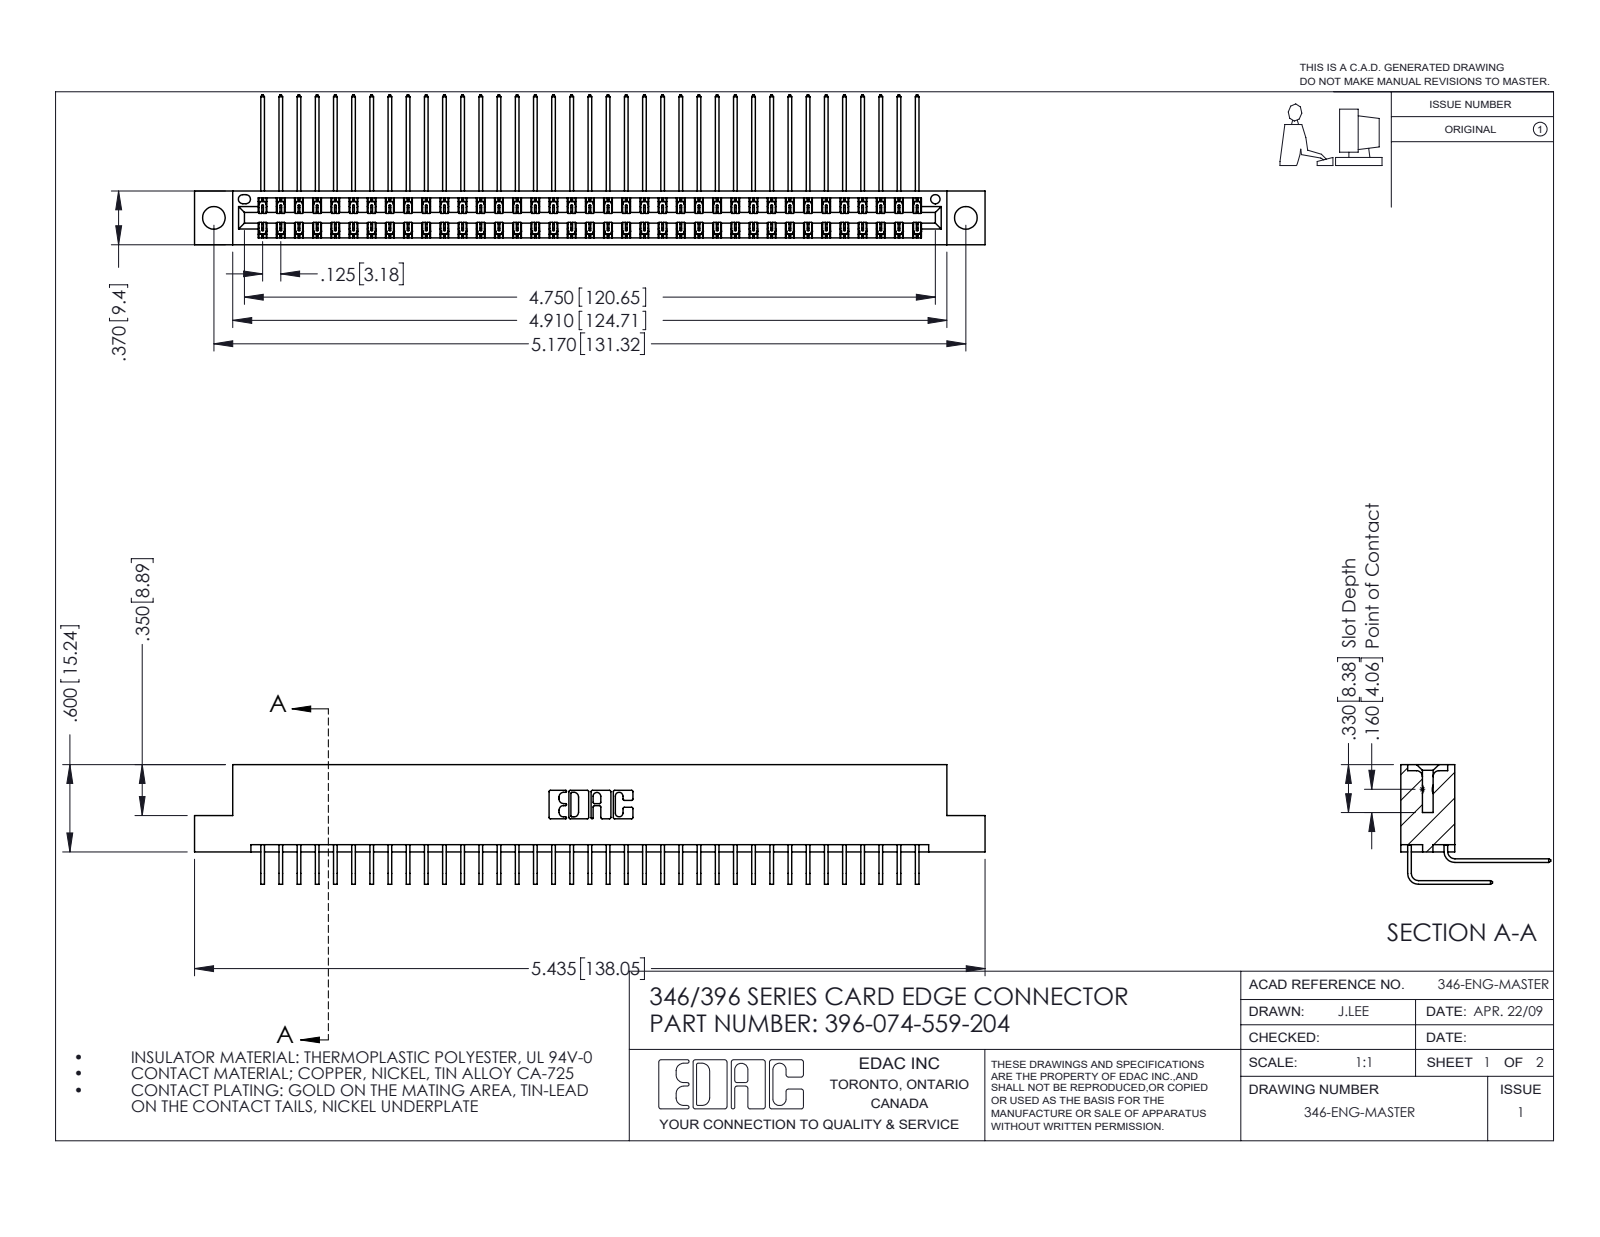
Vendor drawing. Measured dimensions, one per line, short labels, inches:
name: 346 Part_Flush Mounting Lugs - 0.156 Dia-TH; 345-292-001_558 559 Tail - 1; 345-292-001_559 Tail - 2; 396-074-559-204
written by: SolidWorks 2016 (CONFIG_CONTROL_DESIGN)
unit: in
bodies: 75 solids, 4118 faces (2814 planar, 1304 cylindrical, 0 other)
size: 5.435 × 1.03 × 0.823
volume: 0.84 in³; area: 32.08 in²
holes: 2× ⌀0.156, 1× ⌀0.064
rounds: 111× R0.006, 22× R0.01, 6× R0.007, 6× R0.031, 3× R0.026, 2× R0.014, 2× R0.022, 2× R0.024
face distances: 0.048, 0.322, 0.025, 0.37, 0.25, 0.072, 0.298, 0.275, 0.148, 0.222
hole spacings: 0.246, 4.961, 5.17
